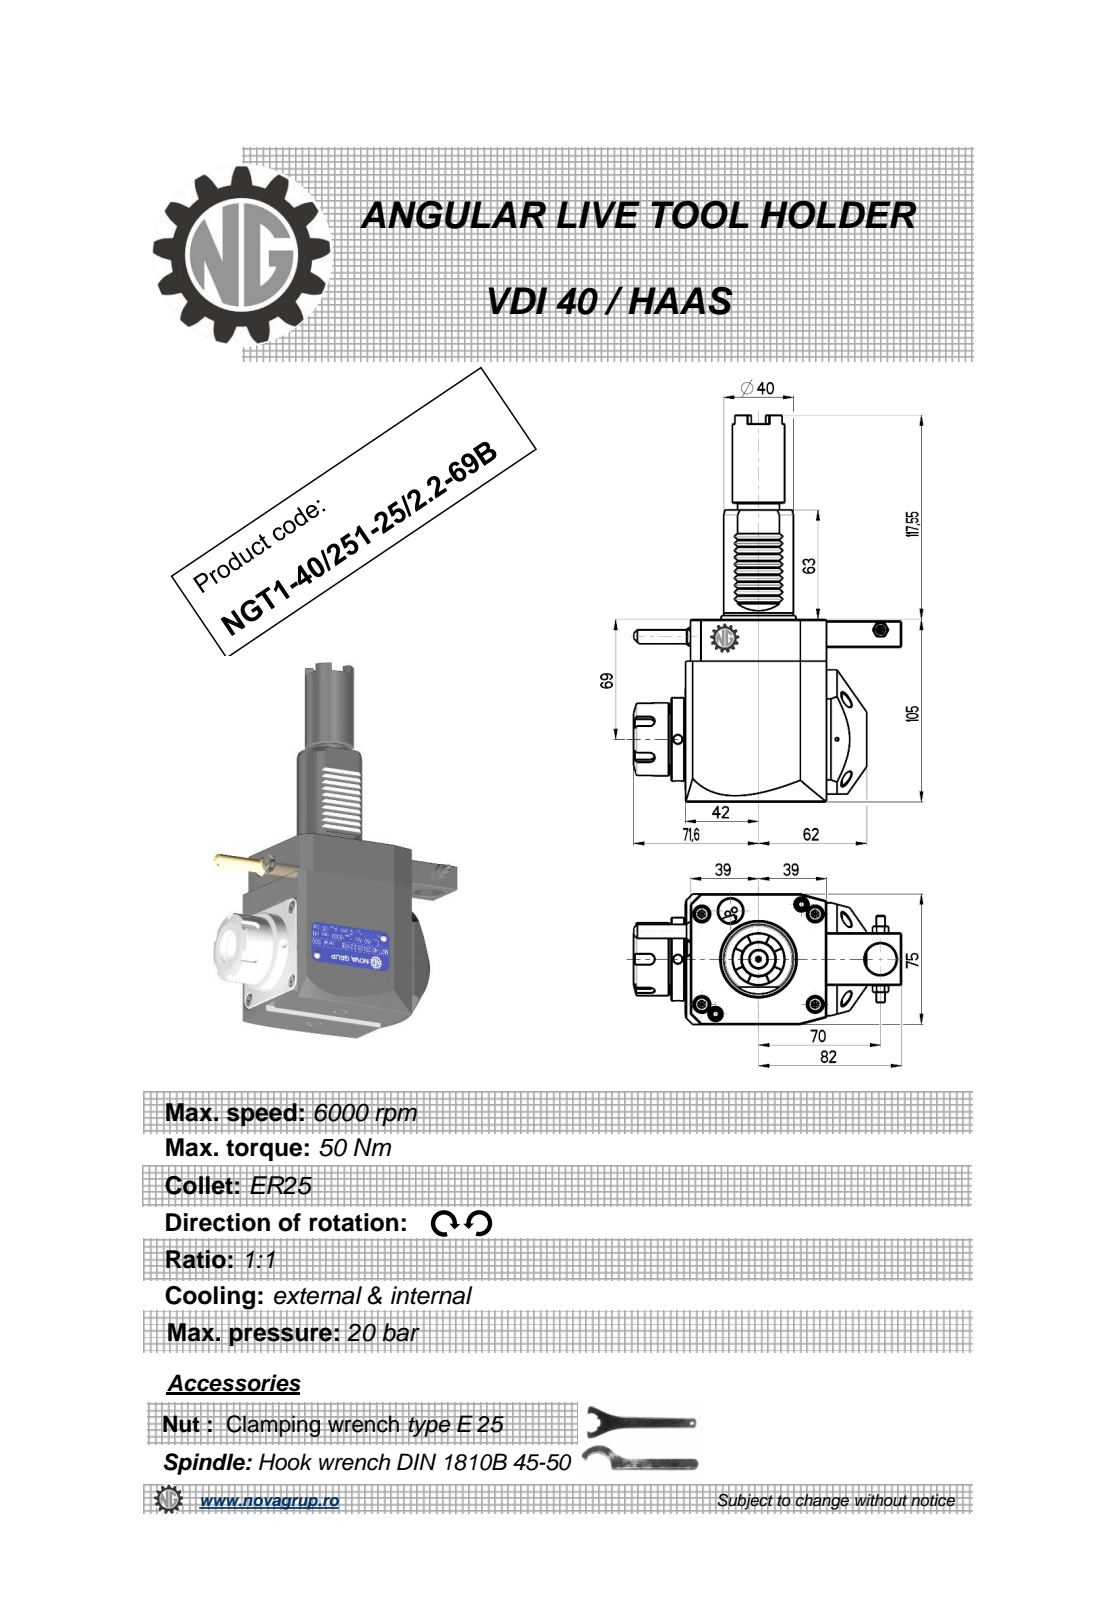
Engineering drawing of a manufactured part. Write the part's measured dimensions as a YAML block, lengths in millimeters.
part_name: "NGT1_40_251_25_2_2_69B"
step_written_by: "PRO/ENGINEER BY PARAMETRIC TECHNOLOGY CORPORATION, 2010280 (CONFIG_CONTROL_DESIGN)"
units: millimeters
bodies: {solids: 1, faces: 476, planar: 223, cylindrical: 94, other: 159}
overall_size: [222.55, 153.6, 76.6]
volume: 851543
surface_area: 73811
round_holes:
  - {diameter: 5, count: 3}
  - {diameter: 3, count: 1}
  - {diameter: 4.2, count: 1}
  - {diameter: 9.5, count: 1}
  - {diameter: 18, count: 1}
  - {diameter: 20.3, count: 1}
round_bosses_or_shafts:
  - {diameter: 48, count: 1}
  - {diameter: 42, count: 1}
  - {diameter: 40, count: 1}
  - {diameter: 37.5, count: 1}
  - {diameter: 33, count: 1}
  - {diameter: 30, count: 1}
  - {diameter: 24, count: 1}
  - {diameter: 10, count: 1}
partial_cylinders:
  - {radius: 0.26, count: 12}
  - {radius: 0.3, count: 10}
  - {radius: 0.2, count: 6}
  - {radius: 3, count: 5}
  - {radius: 0.5, count: 1}
  - {radius: 9.75, count: 1}
  - {radius: 40, count: 1}
face_to_face_distances: [75, 105, 81, 104, 89, 80.8, 1, 101, 3, 2.8]
hole_center_spacings: [16.19, 61.13, 61.5, 116.25, 132.22]
